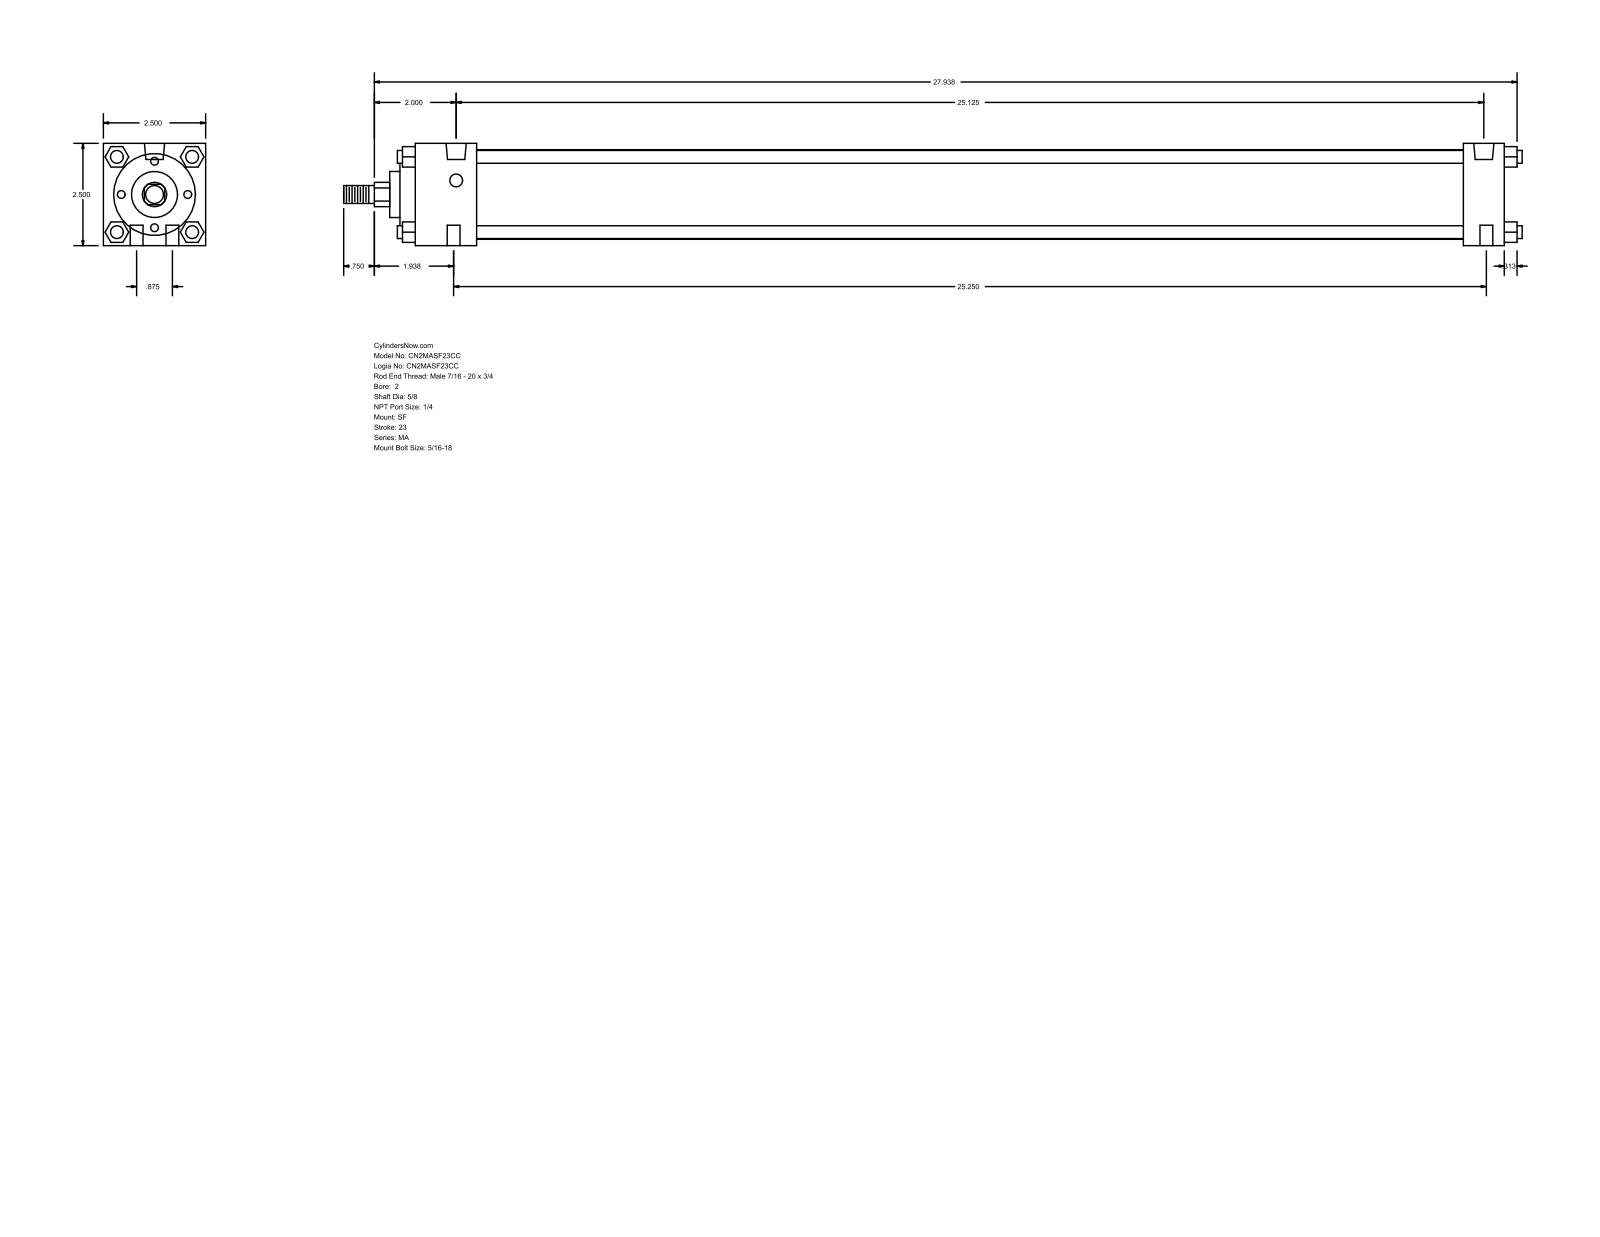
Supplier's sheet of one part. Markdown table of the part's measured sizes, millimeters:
| quantity | value |
| --- | --- |
| part name | MA_SF__0200_0.625 |
| STEP written by | GSSL Pune (CONFIG_CONTROL_DESIGN) |
| units | millimeters |
| bodies | 0 solids, 126 faces (95 planar, 31 cylindrical, 0 other) |
| overall size | 731.84 × 63.5 × 63.5 |
| round holes (diameter × count) | 7.94 × 6, 12.49 × 2 |
| round bosses / shafts (diameter × count) | 7.94 × 4, 55.63 × 1, 50.8 × 1, 28.57 × 1, 15.88 × 1, 11.11 × 1 |
| partial cylindrical surfaces (radius × count) | 7.54 × 1 |
| main face-to-face distances | 63.5, 25.4, 12.7, 38.1, 676.27, 650.87, 612.77, 638.17, 9.52, 47.62 |
| hole center spacings | 11.22, 22.22, 638.18, 639.86, 639.87, 641.35, 641.73 |
